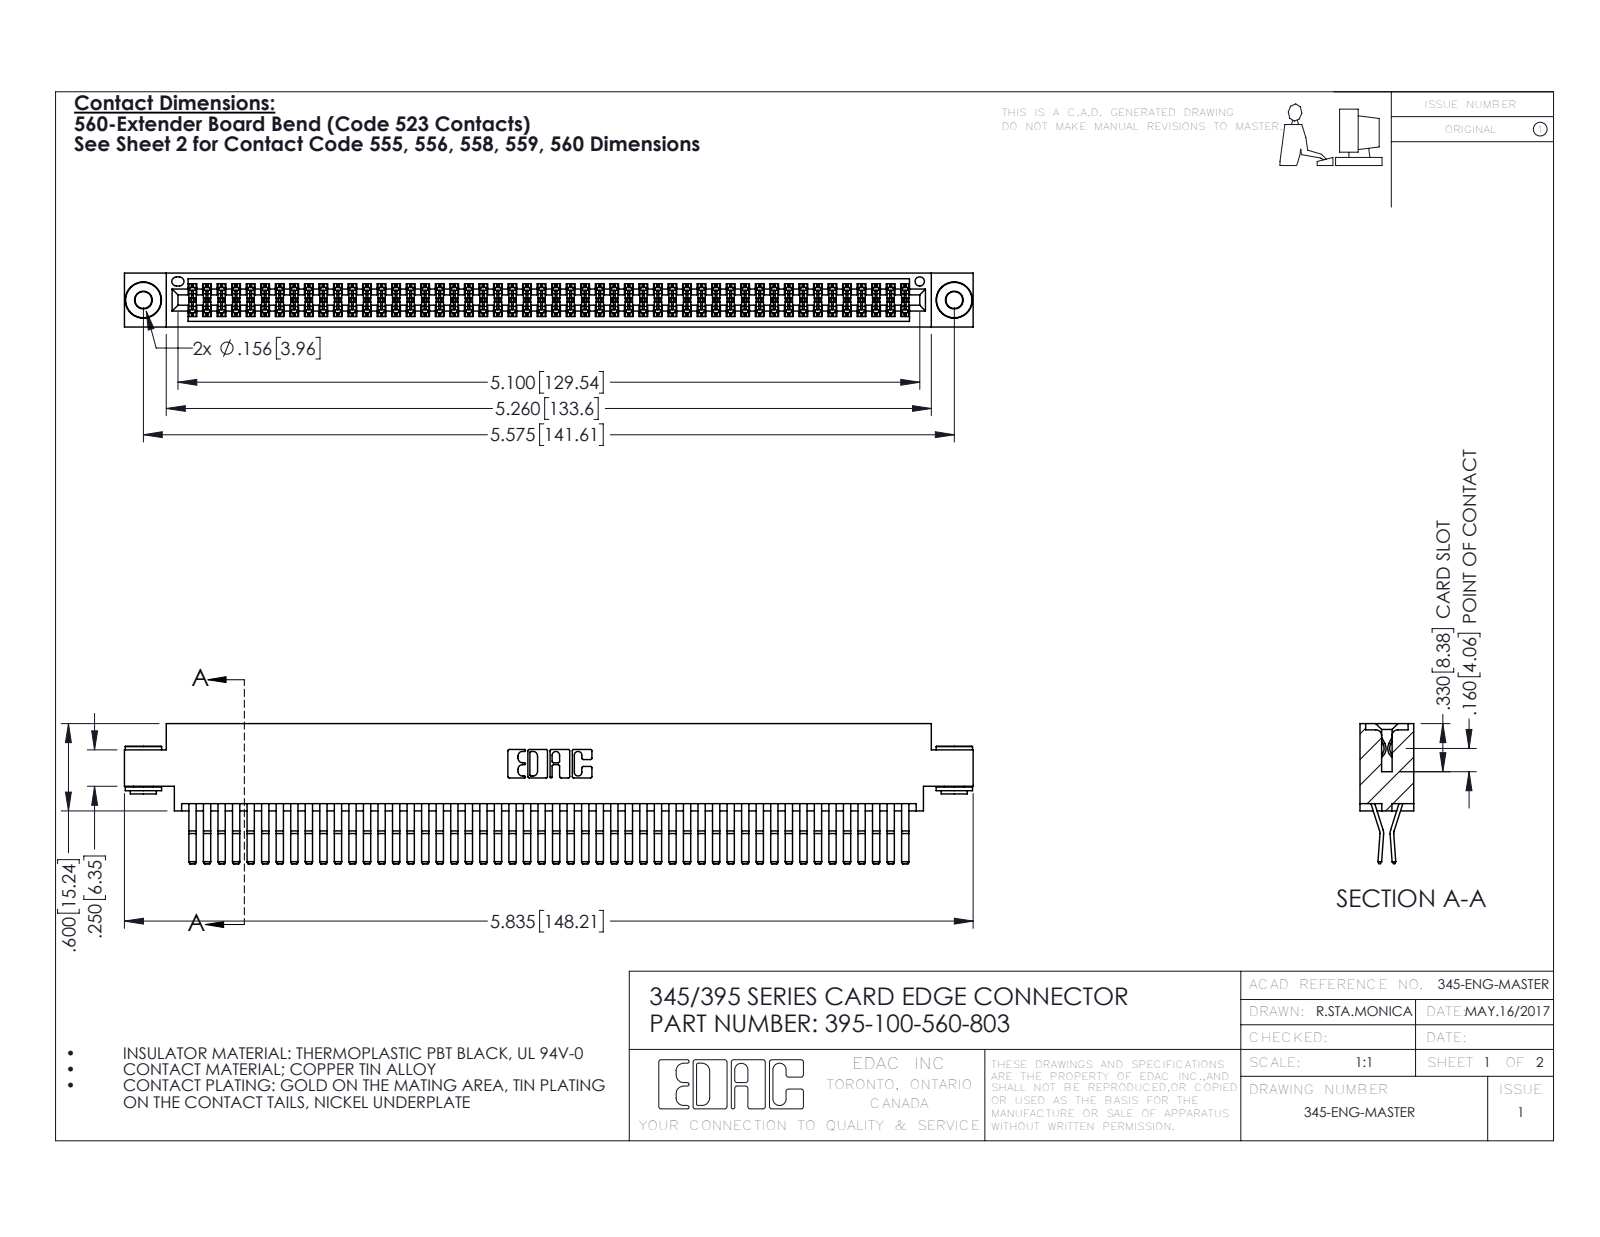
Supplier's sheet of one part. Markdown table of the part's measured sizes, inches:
| quantity | value |
| --- | --- |
| part name | 345-292-001_560 Tail; 345 Part_0.170 Offset - 0.156 Dia-TH; 345-250-002_345-250-002-102; 395-100-560-803 |
| STEP written by | SolidWorks 2016 (CONFIG_CONTROL_DESIGN) |
| units | inches |
| bodies | 103 solids, 5368 faces (3394 planar, 1966 cylindrical, 8 other) |
| overall size | 5.835 × 0.962 × 0.37 |
| volume | 0.917 in³ |
| surface area | 37.84 in² |
| round holes (diameter × count) | 0.116 × 2, 0.156 × 2, 0.064 × 1 |
| round bosses / shafts (diameter × count) | 0.25 × 2, 0.18 × 2, 0.136 × 2 |
| partial cylindrical surfaces (radius × count) | 0.006 × 151, 0.01 × 22, 0.007 × 6, 0.031 × 6, 0.026 × 3, 0.01 × 2, 0.014 × 2, 0.019 × 2 |
| main face-to-face distances | 0.025, 0.072, 0.298, 0.37, 0.2, 0.098, 0.272, 0.225, 0.175, 0.149 |
| hole center spacings | 0.27, 5.339, 5.575 |
